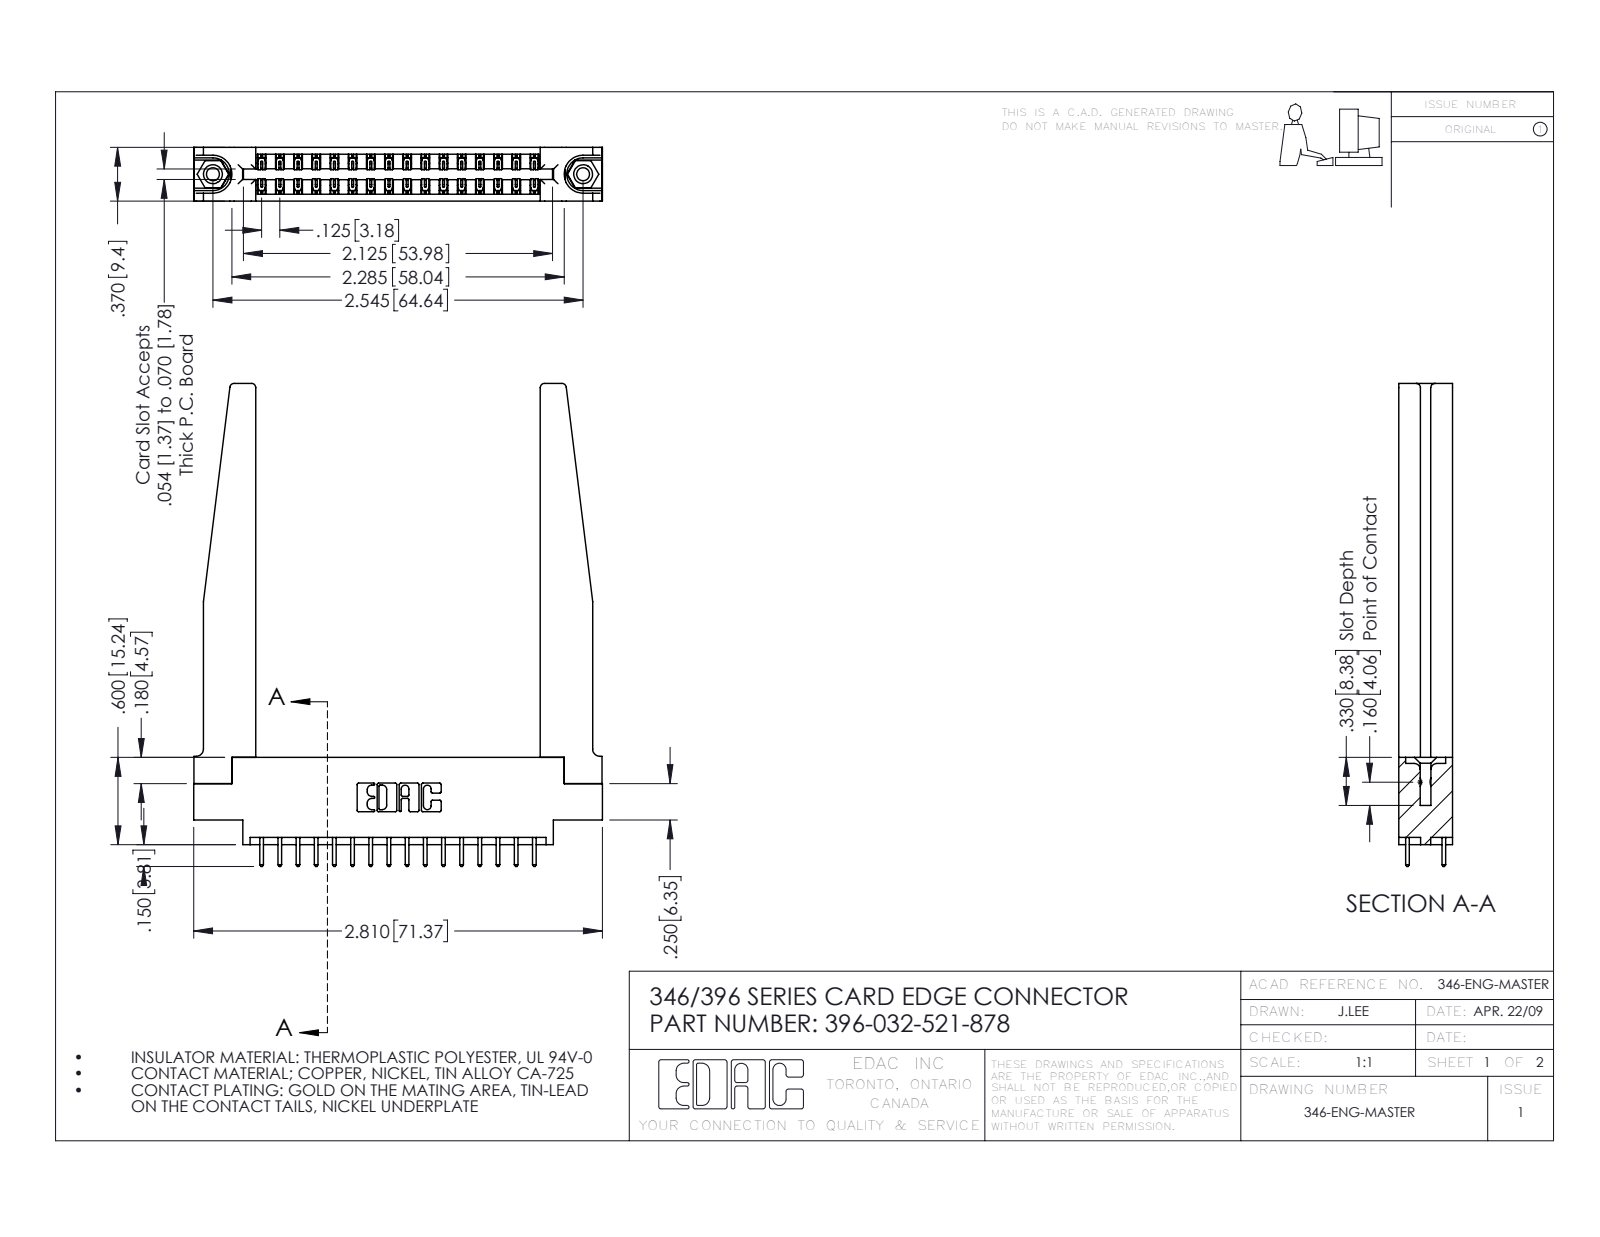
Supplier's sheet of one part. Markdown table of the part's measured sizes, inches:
| quantity | value |
| --- | --- |
| part name | 346-220-078_345-220-078; 345-250-001_345-250-001-102; 346 Part_0.170 Offset - 0.156 Dia-TH; 396-032-521-878 (+1 more) |
| STEP written by | SolidWorks 2016 (CONFIG_CONTROL_DESIGN) |
| units | inches |
| bodies | 37 solids, 2024 faces (1342 planar, 630 cylindrical, 52 other) |
| overall size | 3.32 × 2.81 × 0.37 |
| volume | 0.824 in³ |
| surface area | 23.68 in² |
| round holes (diameter × count) | 0.089 × 2, 0.125 × 2, 0.156 × 2, 0.064 × 1 |
| round bosses / shafts (diameter × count) | 0.155 × 2 |
| partial cylindrical surfaces (radius × count) | 0.006 × 48, 0.01 × 32, 0.01 × 22, 0.03 × 8, 0.007 × 6, 0.031 × 6, 0.026 × 3, 0.014 × 2 |
| main face-to-face distances | 0.37, 0.072, 0.048, 0.322, 0.148, 0.15, 0.25, 0.298, 0.025, 0.102 |
| hole center spacings | 0.246, 2.338, 2.545 |
